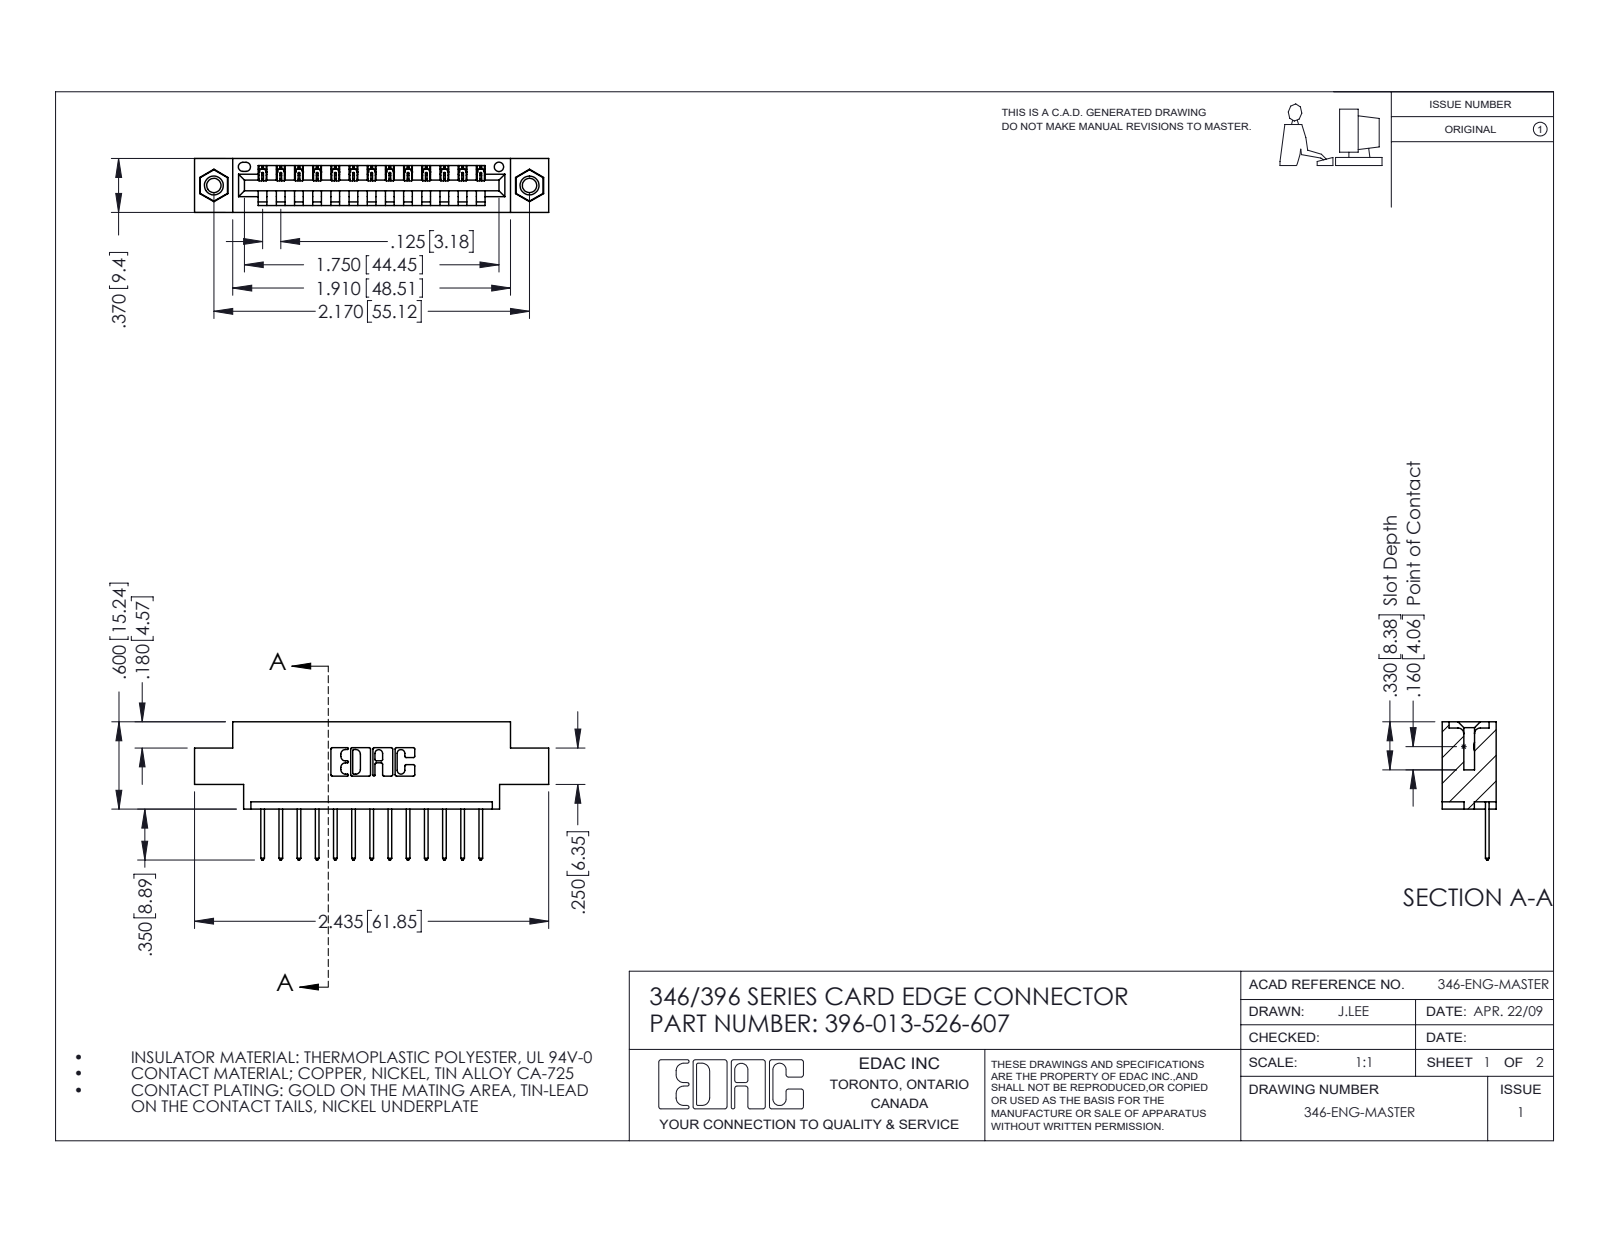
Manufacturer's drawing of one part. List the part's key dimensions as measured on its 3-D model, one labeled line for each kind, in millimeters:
Part name (STEP PRODUCT): 396-013-526-607; 345-292-001_345-293-126; 345-250-001_345-250-005-103; 346 Part_0.170 Offset - 0.156 Dia-TI
STEP written by: SolidWorks 2016 (CONFIG_CONTROL_DESIGN)
Units: millimetres
Bodies: 16 solids, 940 faces (632 planar, 292 cylindrical, 16 other)
Overall size (bounding box): 61.8 × 24.1 × 9.4
Volume: 5 540 mm³ · Surface area: 6 794 mm²
Round holes (diameter × count): ⌀2.5 ×2, ⌀3.2 ×2, ⌀4 ×2, ⌀1.6 ×1
Round bosses / shafts (diameter × count): ⌀3.9 ×2
Partial cylindrical surfaces — rounded edges, fillets, slot ends (radius × count): R0.2 ×26, R0.3 ×26, R0.3 ×22, R0.2 ×6, R0.8 ×6, R0.7 ×3, R0.8 ×2, R1 ×2
Main face-to-face distances: 6.4, 9.4, 1.2, 8.2, 1.8, 7.6, 0.6, 5.6, 3.8, 2.5
Hole centre spacings: 6.2, 49.9, 55.1
